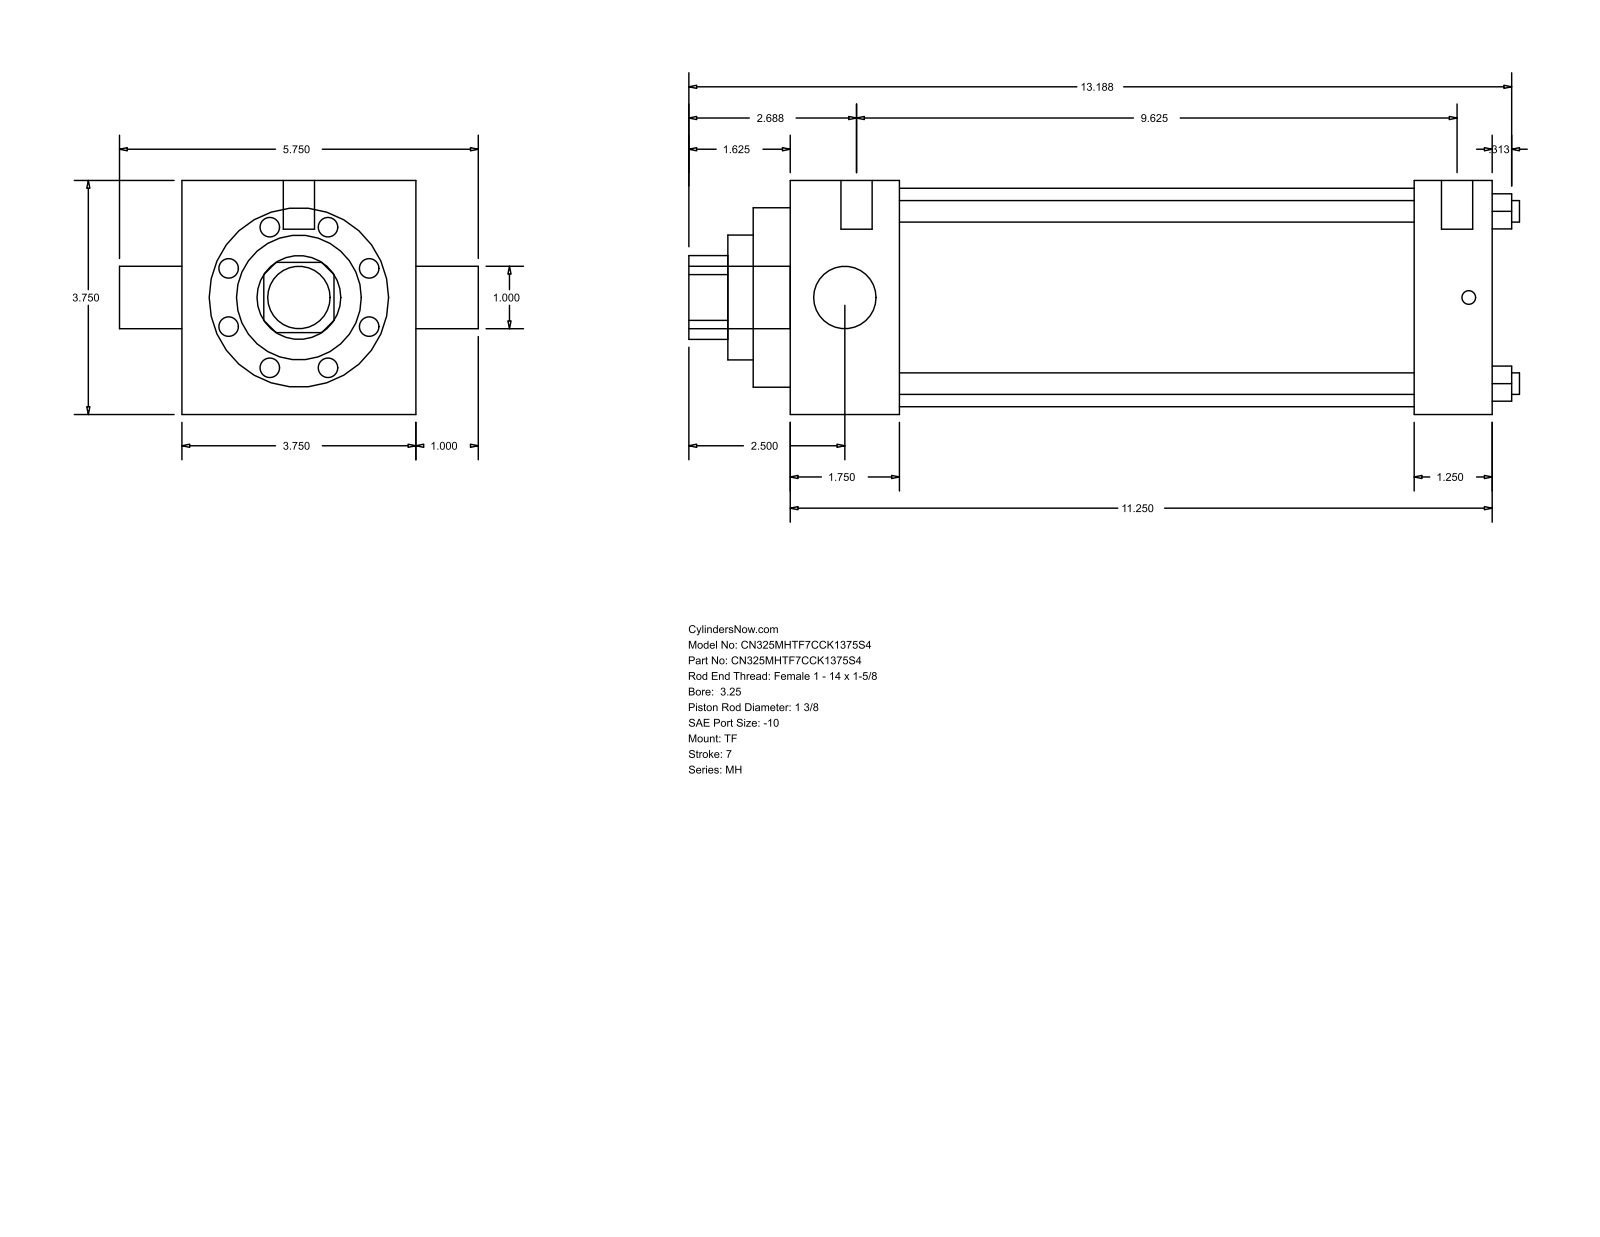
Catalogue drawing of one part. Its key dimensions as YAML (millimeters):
part_name: "MH_TF__0325_1.375"
step_written_by: "GSSL Pune (CONFIG_CONTROL_DESIGN)"
units: millimeters
bodies: {solids: 0, faces: 86, planar: 61, cylindrical: 25, other: 0}
overall_size: [338.14, 146.05, 95.25]
round_holes:
  - {diameter: 8.76, count: 4}
  - {diameter: 25.4, count: 1}
  - {diameter: 34.92, count: 1}
  - {diameter: 50.8, count: 1}
  - {diameter: 73.03, count: 1}
  - {diameter: 88.9, count: 1}
round_bosses_or_shafts:
  - {diameter: 5.56, count: 3}
  - {diameter: 12.7, count: 2}
  - {diameter: 25.4, count: 1}
partial_cylinders:
  - {radius: 17.06, count: 1}
face_to_face_distances: [95.24, 285.75, 44.45, 254, 209.55, 241.3, 31.75, 15.08, 59.53, 269.08]
hole_center_spacings: [49.57, 70.1, 99.14]
